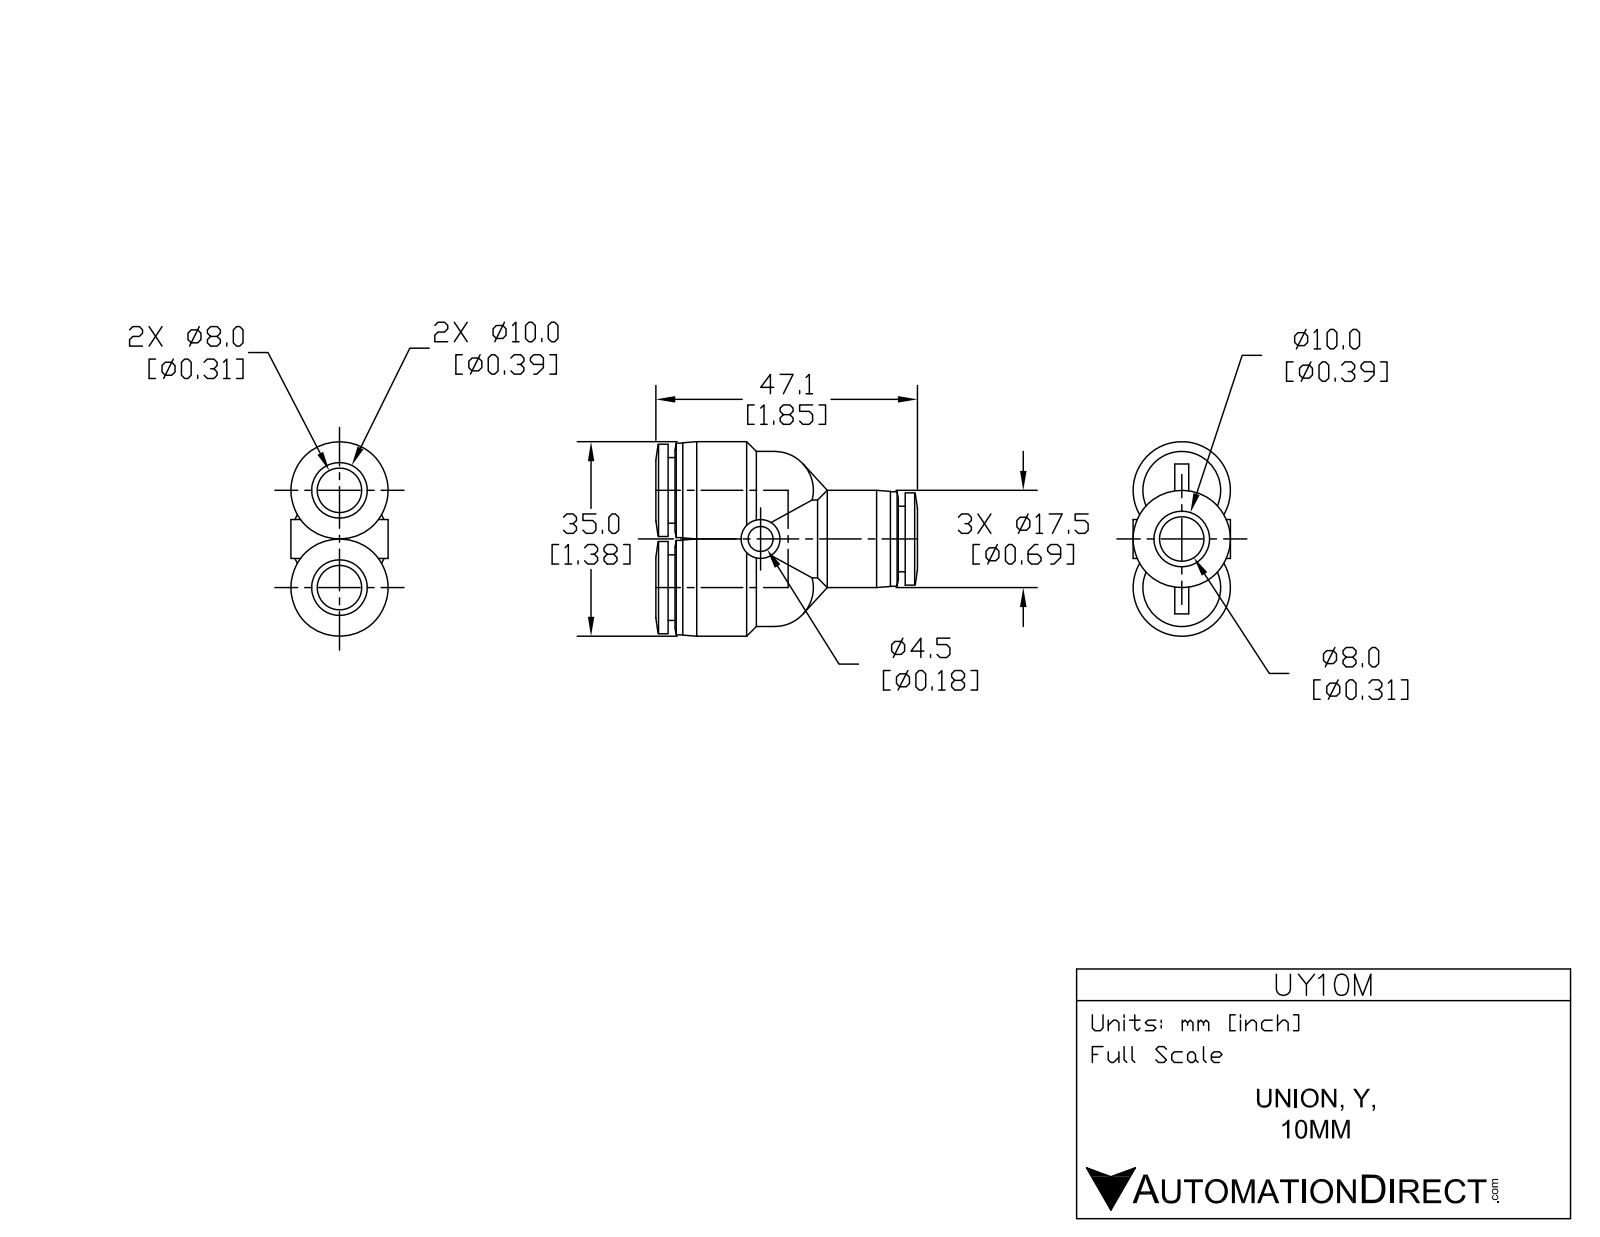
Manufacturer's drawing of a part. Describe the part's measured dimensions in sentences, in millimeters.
The part is named "UY10M". Its 3-D file was written by "SolidWorks 2015 (AUTOMOTIVE_DESIGN)". It is 1 solid with 111 faces: 25 planar, 40 cylindrical and 46 other. Overall it measures 47.2 by 35 by 17.5 millimeters. Its volume is 10 100 cubic millimeters and its surface area 7 574 square millimeters. Round holes: 3 of diameter 10.3, 1 of diameter 4.5. Round bosses or shafts: 3 of diameter 17.5, 3 of diameter 17, 3 of diameter 16.6, 3 of diameter 11.8, 1 of diameter 14, 1 of diameter 7. Partial cylindrical surfaces (rounded edges, fillets, slot ends): 2 of radius 7. The main face-to-face distances are 1.2, 17.7, 16.5, 41.6, 25.1, 23.9, 42.8, 40.3, 7.4, 7.5. The hole center spacings are 8.7, 17.5.
